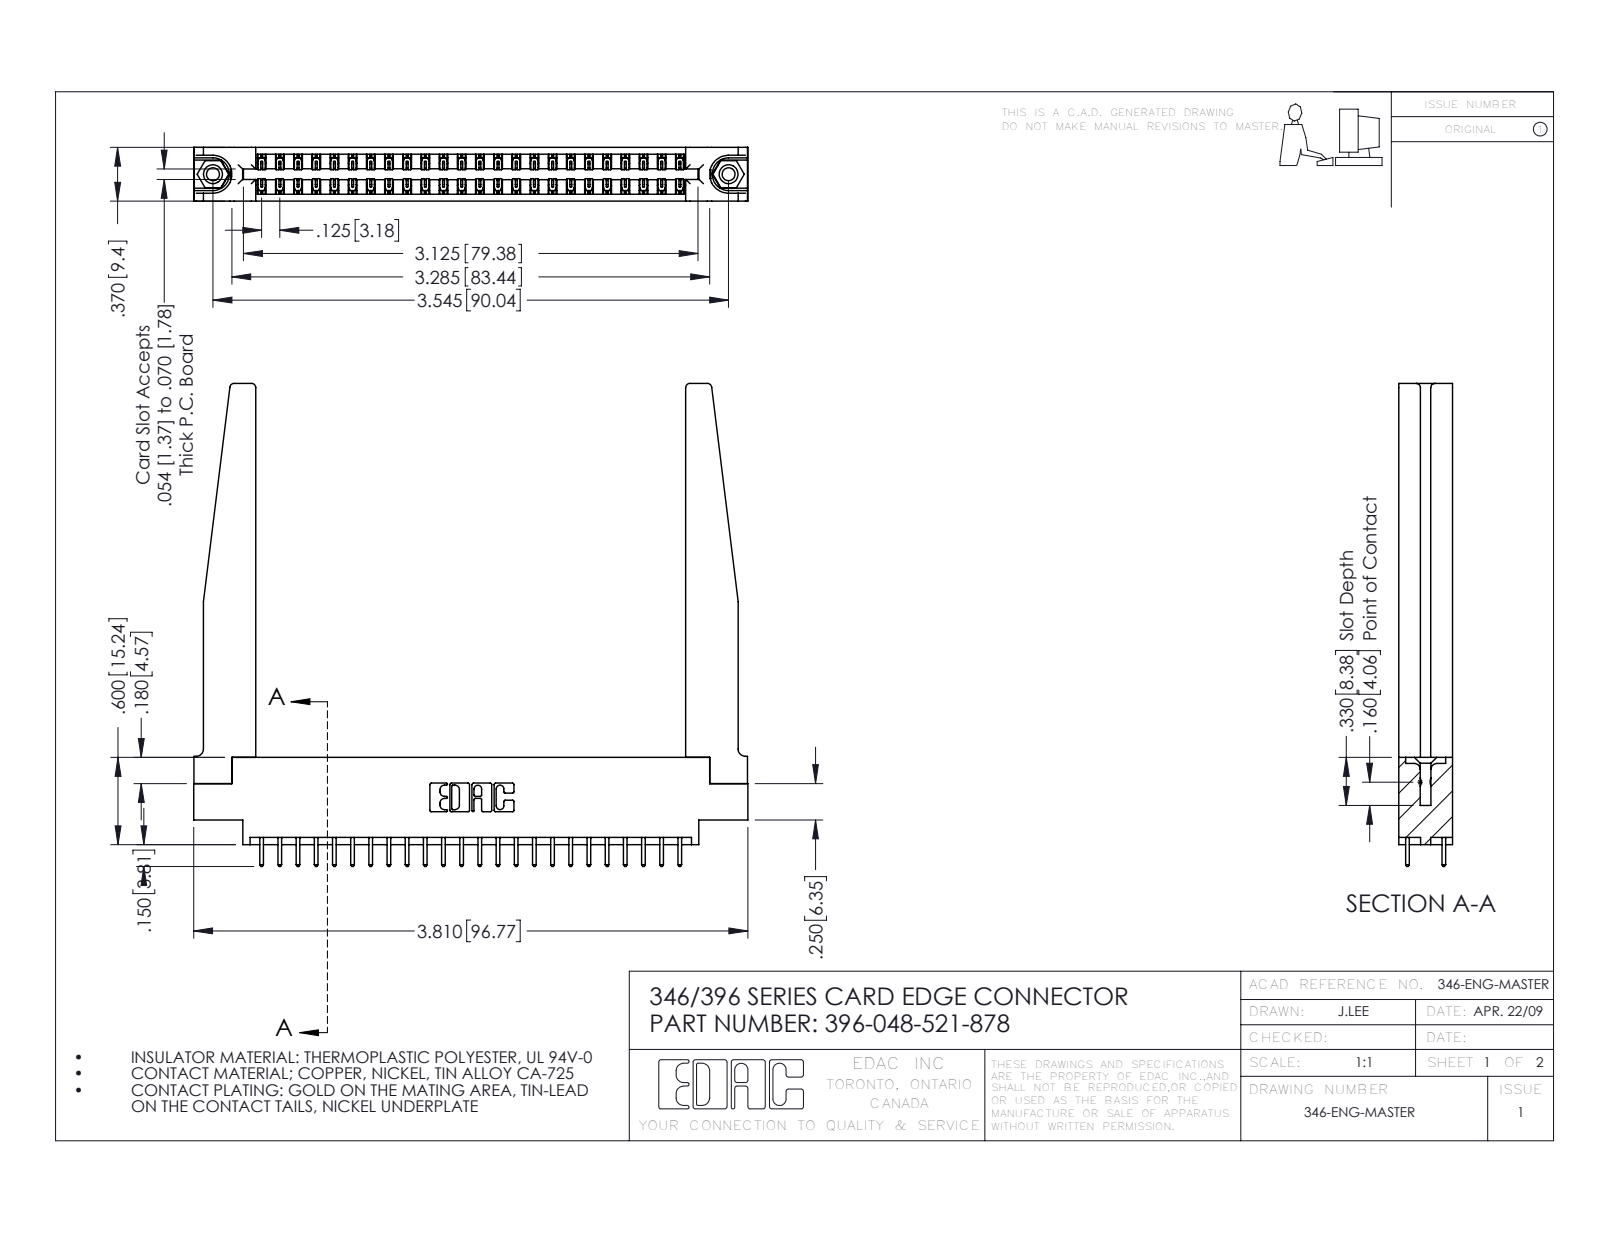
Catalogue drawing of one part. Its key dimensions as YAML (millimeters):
part_name: "346-220-078_345-220-078; 396-048-521-878; 345-250-001_345-250-001-102; 346 Part_0.170 Offset - 0.156 Dia-TH (+1 more)"
step_written_by: "SolidWorks 2016 (CONFIG_CONTROL_DESIGN)"
units: millimeters
bodies: {solids: 53, faces: 2856, planar: 1902, cylindrical: 902, other: 52}
overall_size: [96.8, 84.3, 9.4]
volume: 16000
surface_area: 18850
round_holes:
  - {diameter: 2.3, count: 2}
  - {diameter: 3.2, count: 2}
  - {diameter: 4, count: 2}
  - {diameter: 1.6, count: 1}
round_bosses_or_shafts:
  - {diameter: 3.9, count: 2}
partial_cylinders:
  - {radius: 0.2, count: 72}
  - {radius: 0.3, count: 48}
  - {radius: 0.3, count: 22}
  - {radius: 0.8, count: 8}
  - {radius: 0.2, count: 6}
  - {radius: 0.8, count: 6}
  - {radius: 0.7, count: 3}
  - {radius: 0.4, count: 2}
face_to_face_distances: [9.4, 1.2, 8.2, 1.8, 3.8, 3.8, 6.4, 7.6, 0.6, 7]
hole_center_spacings: [6.2, 84.8, 90]
